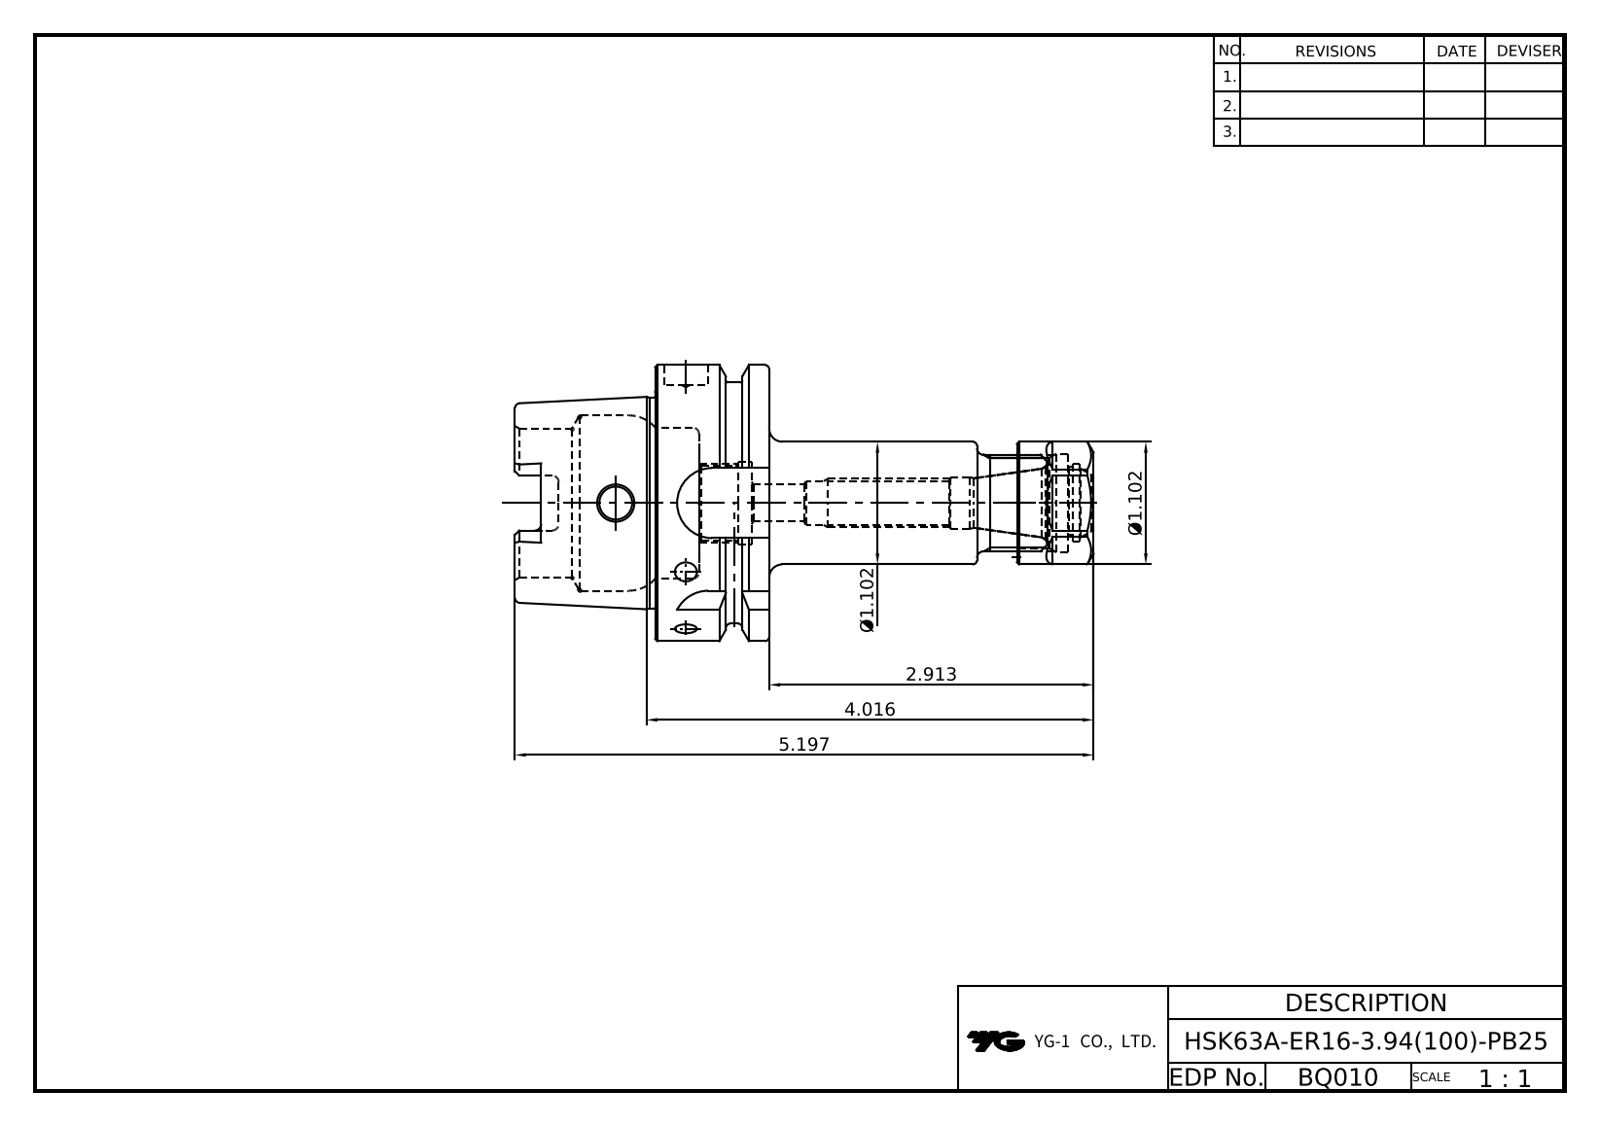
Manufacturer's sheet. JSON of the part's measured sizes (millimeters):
{"part_name": "HSK63A-ER16-100; ER16NUT_3D_20140325; HSK63A-ER16-100_ASM", "step_written_by": "PRO/ENGINEER BY PARAMETRIC TECHNOLOGY CORPORATION, 2012130 (CONFIG_CONTROL_DESIGN)", "units": "millimeters", "bodies": {"solids": 2, "faces": 224, "planar": 75, "cylindrical": 67, "other": 82}, "overall_size": [132, 63, 63], "volume_mm3": 115884, "surface_area_mm2": 34535, "round_holes": [[10, 2], [1, 1], [7.5, 1], [8.5, 1], [10.5, 1], [12.8, 1], [17, 1], [17.7, 1], [18, 1], [19, 1], [20.6, 1], [22.5, 1]], "round_bosses_or_shafts": [[63, 1], [55, 1], [48.04, 1], [28, 1], [22, 1]], "partial_cylinders_radius": [[1.5, 6], [2.88, 4], [8, 4], [7.7, 2]], "face_to_face_distances": [26, 16, 10, 32, 6.12, 9.88, 42, 58, 25, 53], "hole_center_spacings": [12]}
